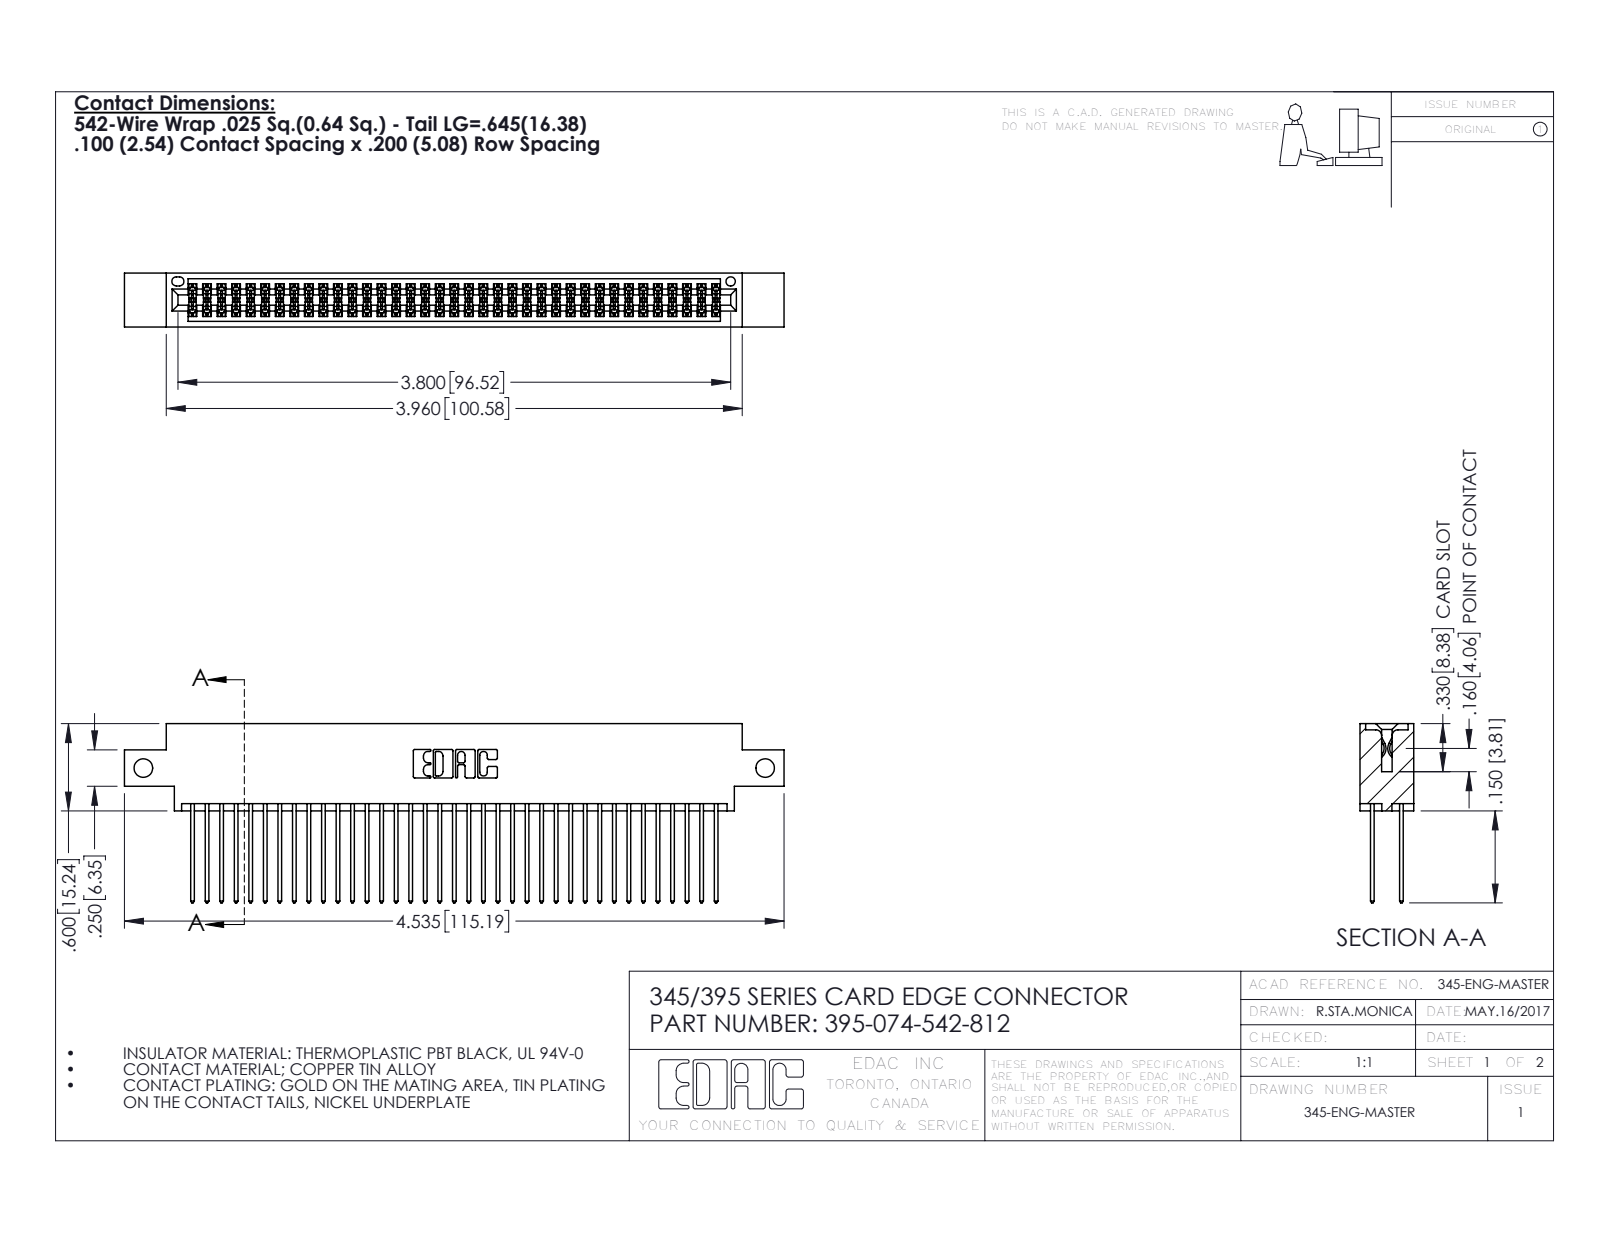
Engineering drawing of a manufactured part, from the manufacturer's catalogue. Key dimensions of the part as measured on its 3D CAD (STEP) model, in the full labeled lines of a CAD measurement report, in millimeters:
Part name (STEP PRODUCT): 395-074-542-812; 345-292-001_345-293-142; 345 Part_0.170 Offset - Side Mount
STEP written by: SolidWorks 2016 (CONFIG_CONTROL_DESIGN)
Units: millimetres
Bodies: 75 solids, 3830 faces (2526 planar, 1304 cylindrical, 0 other)
Overall size (bounding box): 115.2 × 31.3 × 9.4
Volume: 11 300 mm³ · Surface area: 18 210 mm²
Round holes (diameter × count): ⌀3.3 ×2, ⌀1.6 ×1
Partial cylindrical surfaces — rounded edges, fillets, slot ends (radius × count): R0.2 ×111, R0.3 ×74, R0.3 ×22, R0.2 ×6, R0.8 ×6, R0.7 ×3, R0.4 ×2, R0.5 ×2
Main face-to-face distances: 7.6, 1.8, 5.1, 2.5, 6.9, 0.6, 9.4, 5.7, 4.4, 3.8
Hole centre spacings: 108.6
